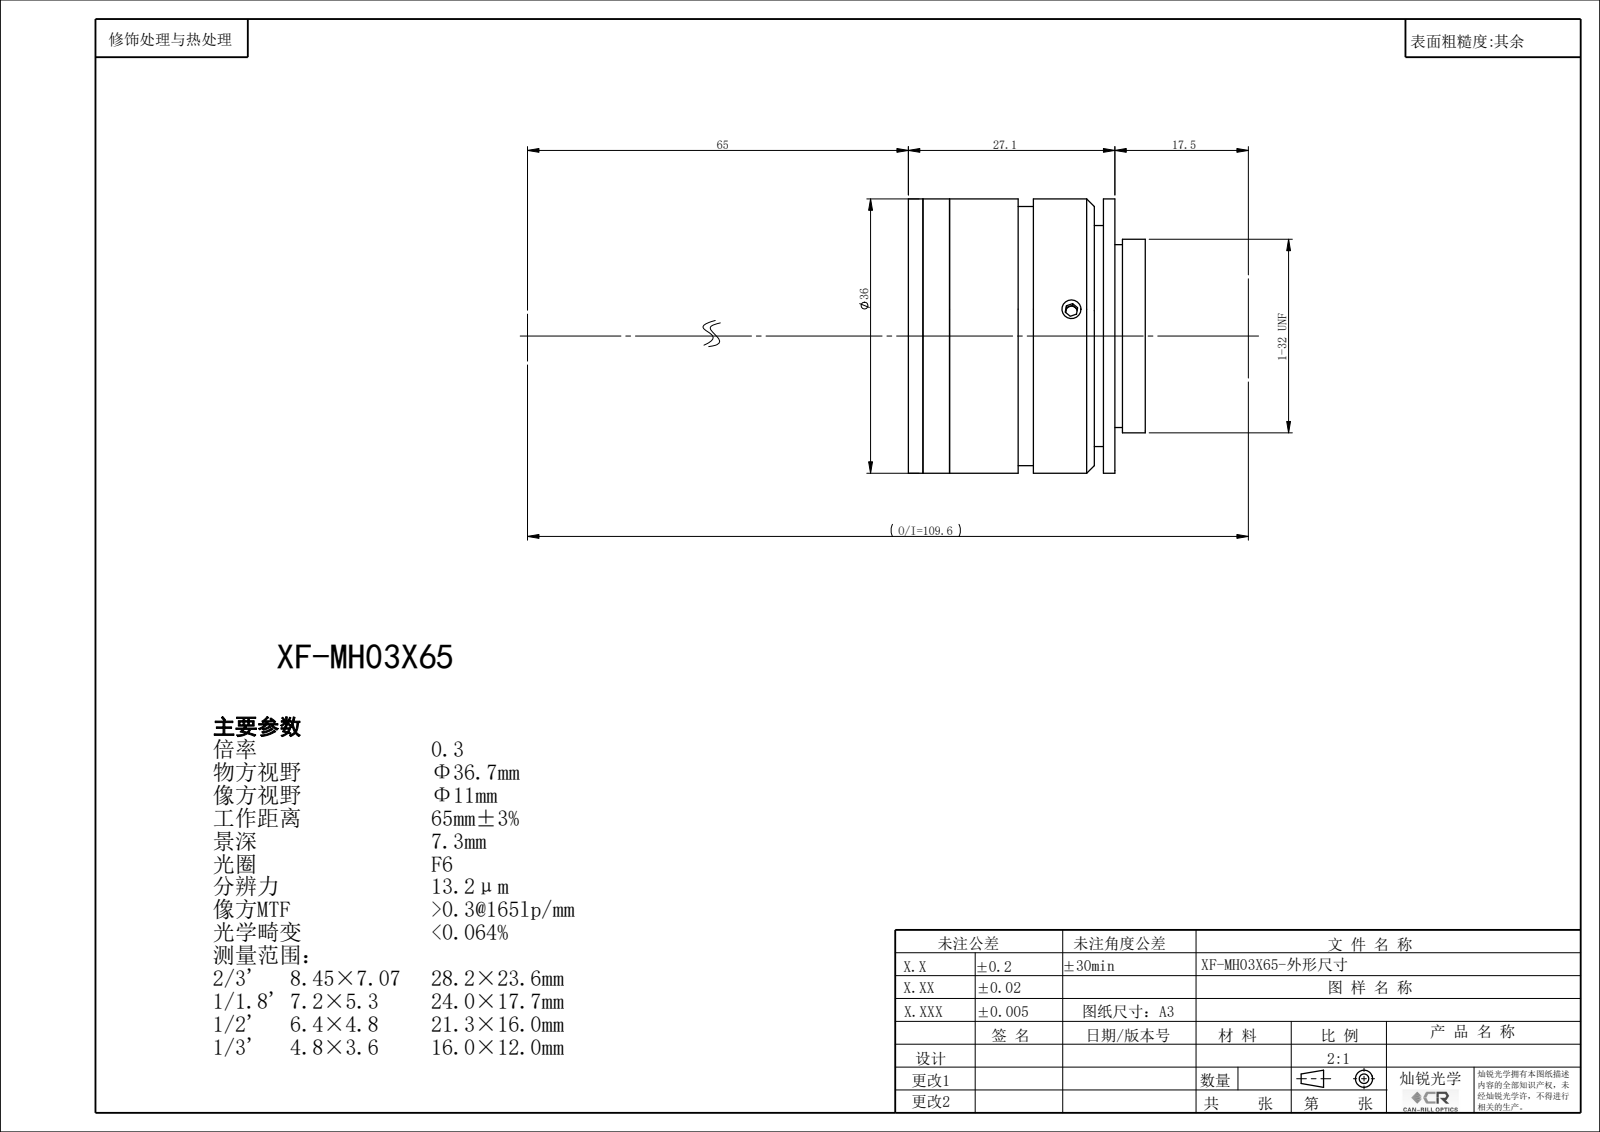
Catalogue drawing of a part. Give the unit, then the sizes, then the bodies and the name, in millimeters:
Units: millimetres
Overall size (bounding box): 36.53 × 36 × 30.91
Round holes (diameter × count): ⌀1 ×2, ⌀7 ×1, ⌀8.4 ×1, ⌀20 ×1, ⌀21 ×1, ⌀24.9 ×1
Round bosses / shafts (diameter × count): ⌀36 ×1, ⌀25.4 ×1, ⌀9 ×1, ⌀4.5 ×1
Partial cylindrical surfaces — rounded edges, fillets, slot ends (radius × count): R25 ×5, R2.5 ×1
Main face-to-face distances: 7, 1, 3.5, 15, 14, 25, 21.5, 1.91, 5.41, 26.91
Hole centre spacings: 11.5, 23
Bodies: 0 solids, 99 faces (41 planar, 41 cylindrical, 17 other)
Part name (STEP PRODUCT): XF-NH03X65
STEP written by: SolidWorks 2014 (CONFIG_CONTROL_DESIGN)
